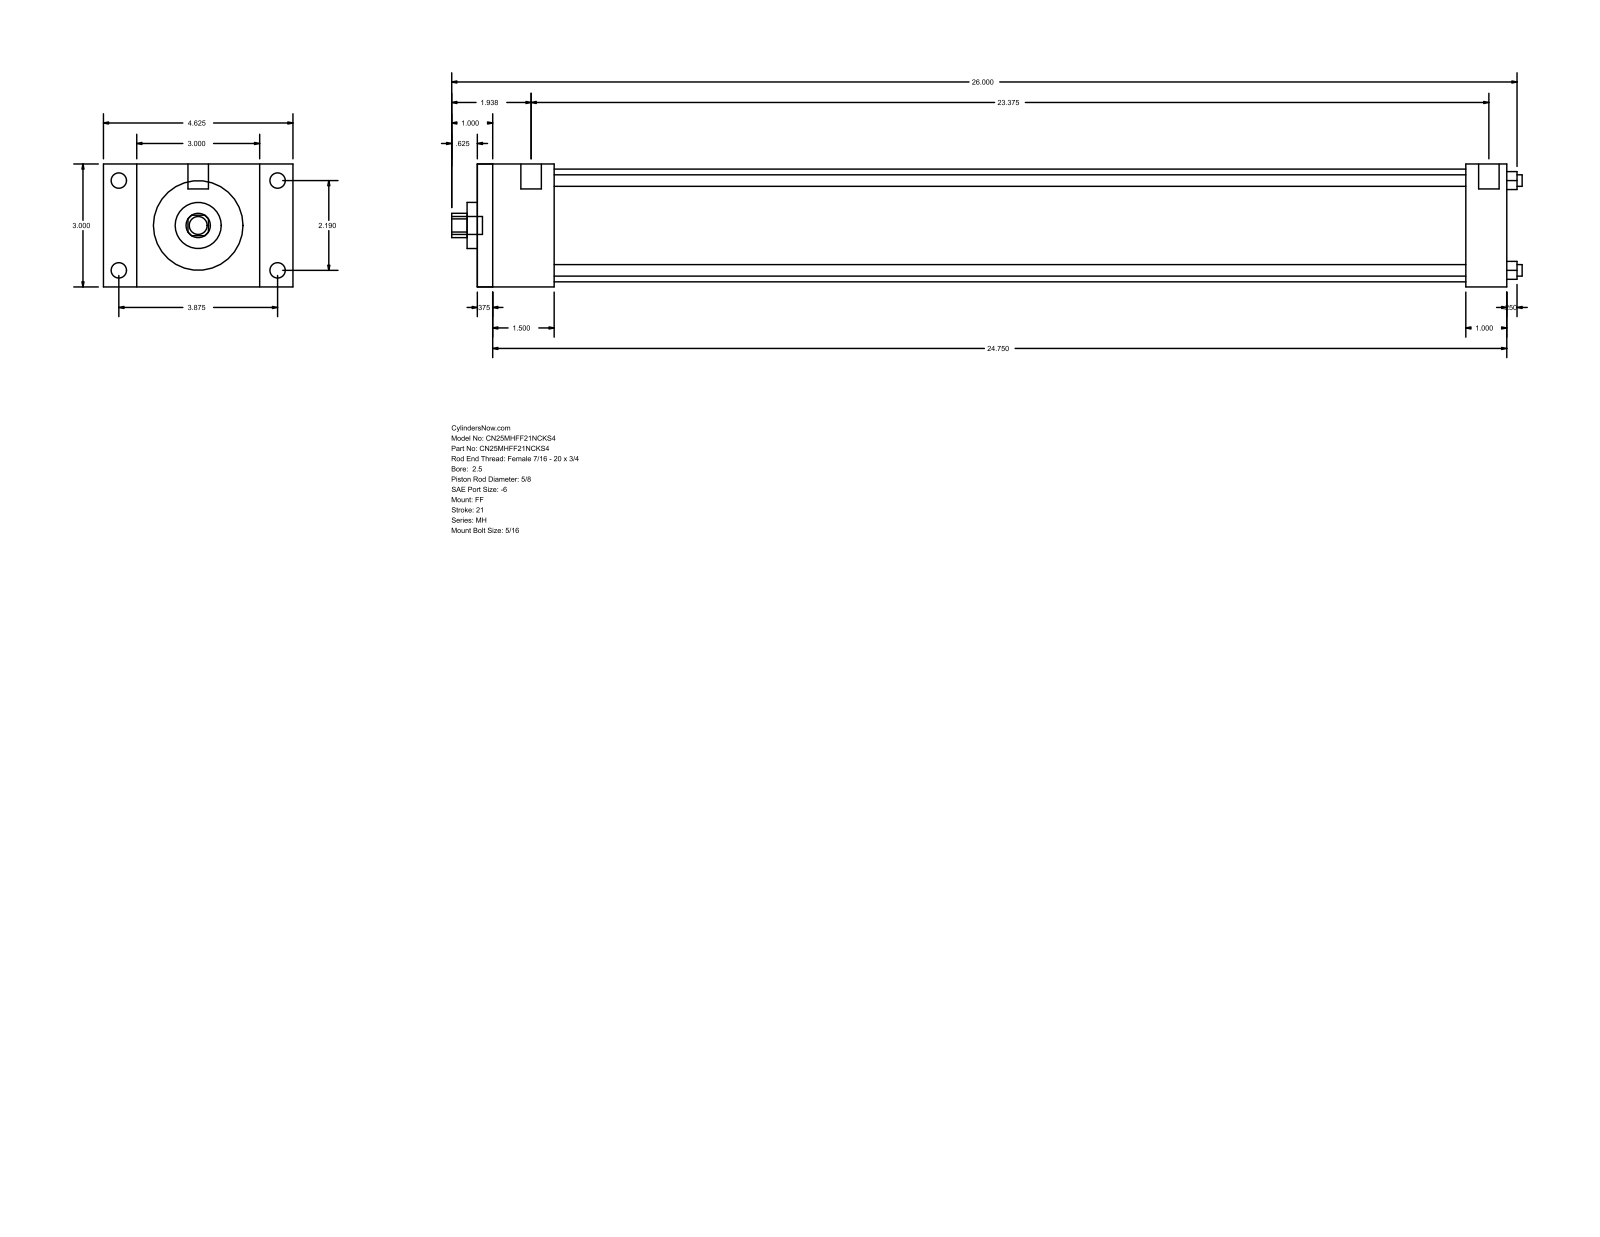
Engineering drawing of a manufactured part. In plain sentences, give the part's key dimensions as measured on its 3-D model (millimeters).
The part is named "MH_FF__0250_0.625". Its 3-D file was written by "GSSL Pune (CONFIG_CONTROL_DESIGN)". It is 0 solids with 92 faces: 64 planar, 28 cylindrical and 0 other. Overall it measures 663.58 by 117.47 by 76.2 millimeters. Round holes: 4 of diameter 7.14, 1 of diameter 15.88, 1 of diameter 28.57, 1 of diameter 69.85. Round bosses or shafts: 4 of diameter 9.53, 4 of diameter 5.56, 2 of diameter 12.7, 1 of diameter 11.11. Partial cylindrical surfaces (rounded edges, fillets, slot ends): 1 of radius 7.54. The main face-to-face distances are 76.2, 638.17, 9.52, 628.65, 25.4, 47.62, 612.77, 38.1, 603.25, 565.15. The hole center spacings are 39.33, 55.62, 78.66.
